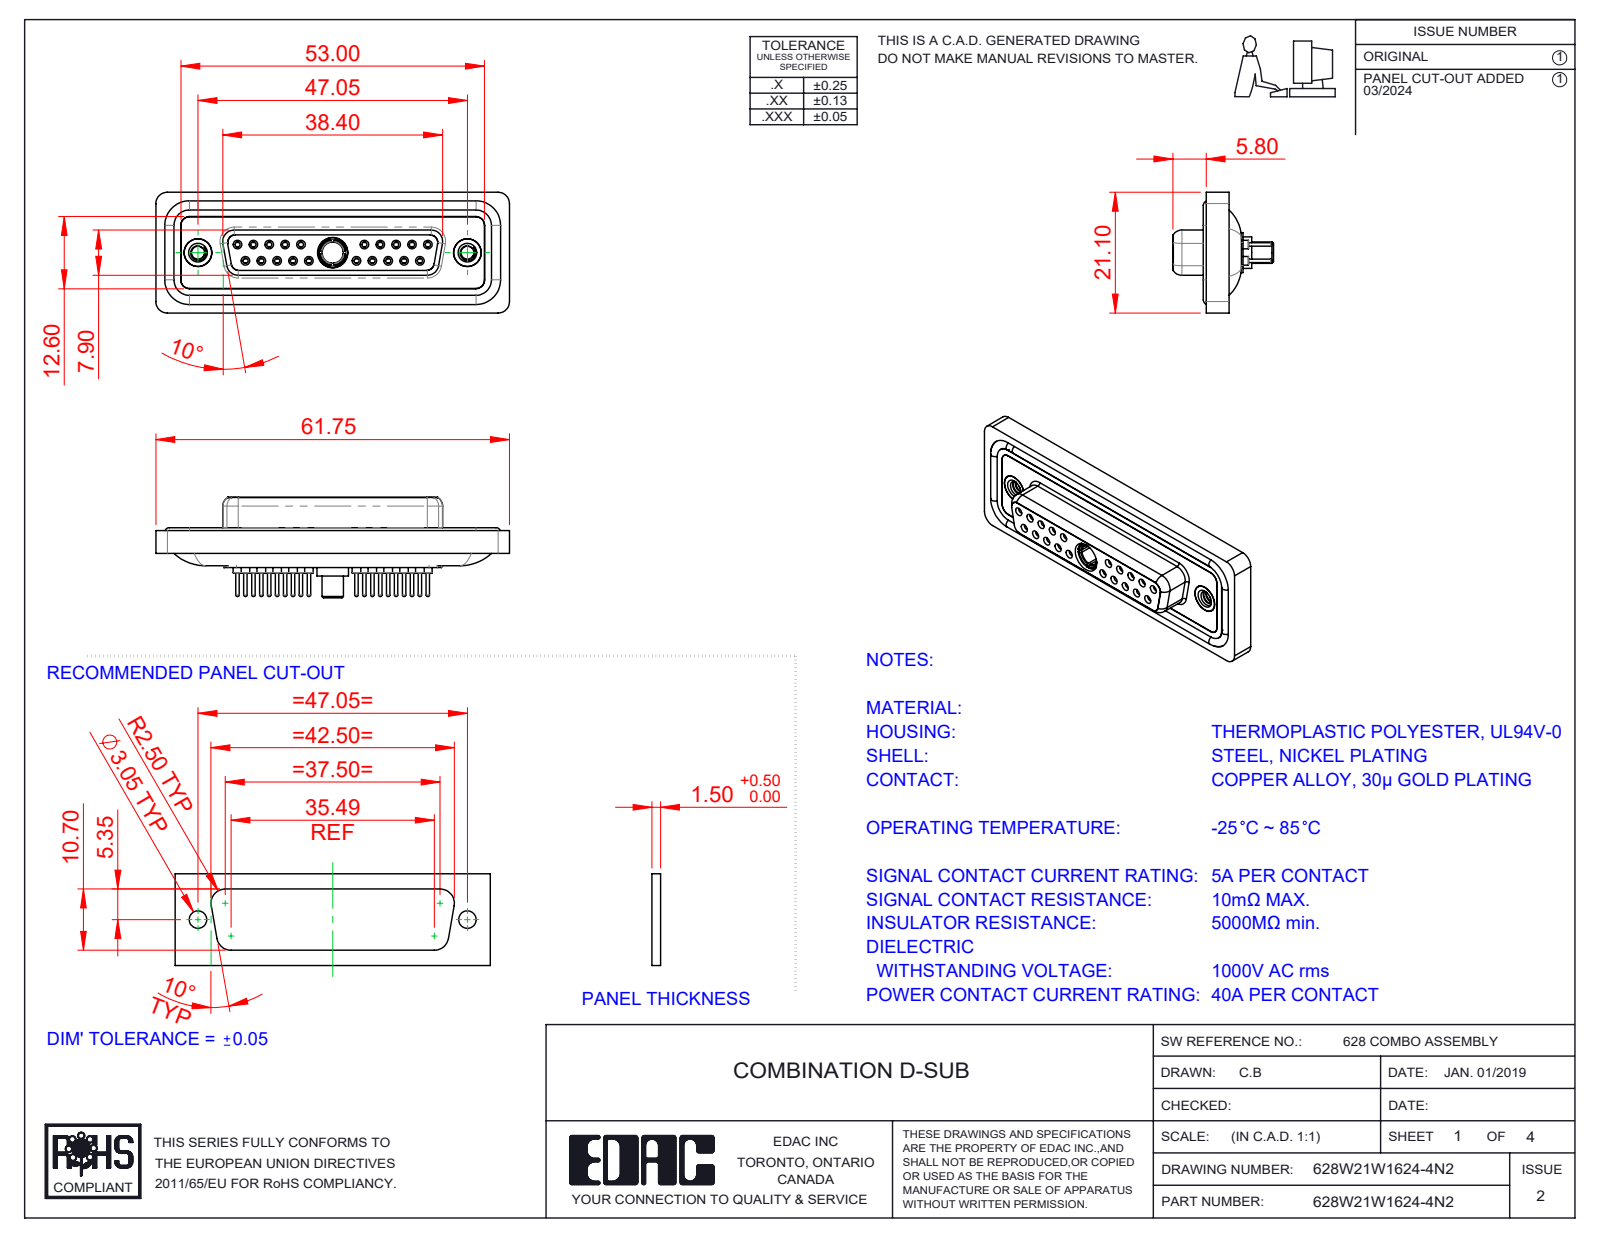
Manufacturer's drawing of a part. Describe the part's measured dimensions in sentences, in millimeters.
The part is named "628Combo Threaded Rivet_2; 628W21W1624-4N2; 628Combo Shell Rear_25 Contacts; 628Combo Contact Row 1_24 (+5 more)". Its 3-D file was written by "SolidWorks 2023 (CONFIG_CONTROL_DESIGN)". It is 29 solids with 1560 faces: 434 planar, 591 cylindrical and 535 other. Overall it measures 61.75 by 21.1 by 17.55 millimeters. Its volume is 8 393 cubic millimeters and its surface area 14 013 square millimeters. Round holes: 20 of diameter 0.9, 20 of diameter 1.1, 20 of diameter 1.5, 20 of diameter 2, 10 of diameter 1.6, 10 of diameter 1.7, 3 of diameter 4.85, 2 of diameter 2.26, 2 of diameter 4, 2 of diameter 4.05, 2 of diameter 5, 1 of diameter 3.7. Round bosses or shafts: 20 of diameter 2.2, 20 of diameter 0.6, 14 of diameter 1.6, 2 of diameter 4.95, 2 of diameter 4.8, 1 of diameter 5.5, 1 of diameter 5.2, 1 of diameter 4.96. Partial cylindrical surfaces (rounded edges, fillets, slot ends): 22 of radius 1.5, 18 of radius 2, 8 of radius 1.35, 8 of radius 1.6, 4 of radius 0.25, 4 of radius 0.5, 4 of radius 0.6, 4 of radius 0.65. The main face-to-face distances are 0.4, 1.8, 7.45, 6.6, 5.65, 0.5, 1.6, 7.05, 2.9, 1.1. The hole center spacings are 3.16, 2.77, 5.54, 5.03, 8.31, 7.48, 16.62, 19.39.
